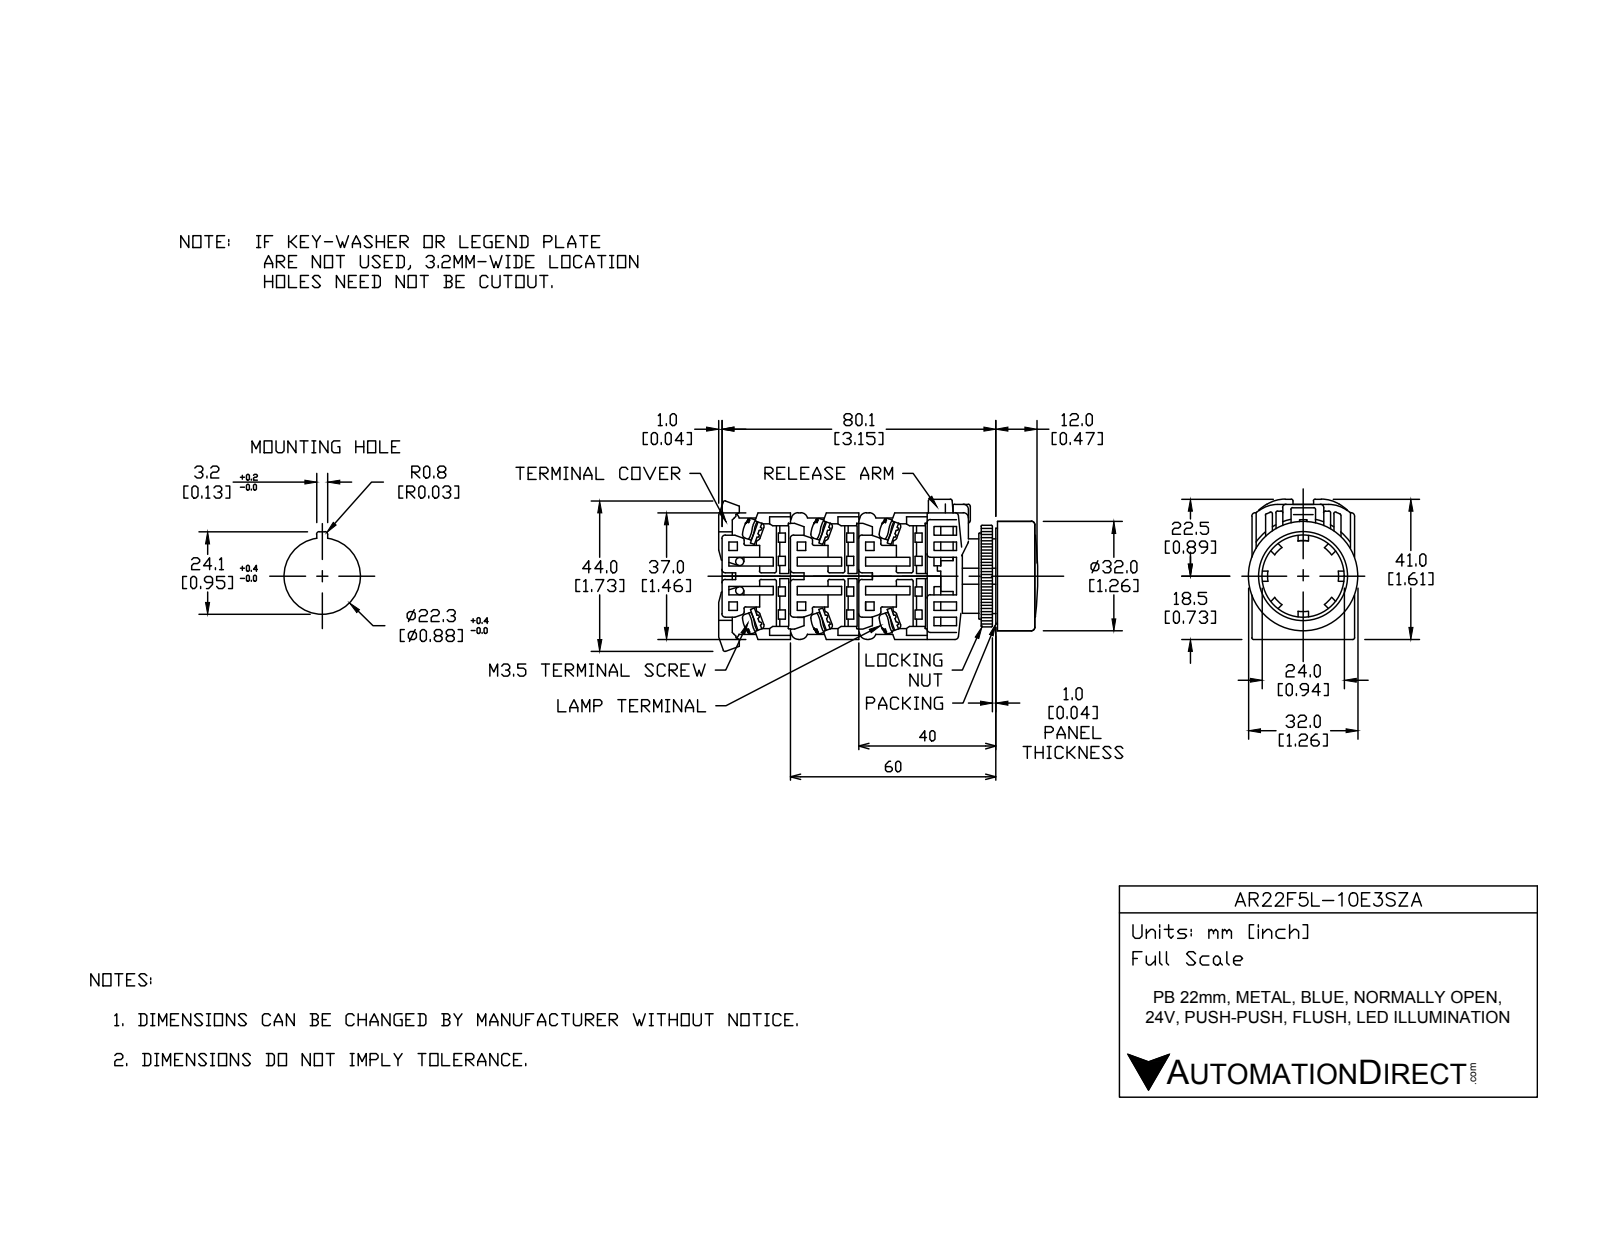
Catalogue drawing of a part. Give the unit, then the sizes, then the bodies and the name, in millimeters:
Units: millimetres
Overall size (bounding box): 52.75 × 43.81 × 32
Round holes (diameter × count): ⌀21.8 ×1, ⌀22 ×1, ⌀25 ×1, ⌀31 ×1
Round bosses / shafts (diameter × count): ⌀5 ×4, ⌀32 ×1, ⌀30.5 ×1, ⌀29.8 ×1, ⌀24 ×1, ⌀23.8 ×1, ⌀21.75 ×1, ⌀17 ×1
Partial cylindrical surfaces — rounded edges, fillets, slot ends (radius × count): R0.5 ×39, R1.75 ×8, R5 ×4, R4 ×2, R16.59 ×1, R17.59 ×1
Main face-to-face distances: 1, 18, 28.5, 48.5, 20, 29, 3, 2, 21, 0.5
Volume: 36 367 mm³ · Surface area: 24 064 mm²
Bodies: 18 solids, 475 faces (329 planar, 111 cylindrical, 35 other)
Part name (STEP PRODUCT): AR22F5L-10E3SZA
STEP written by: SolidWorks 2017 (AUTOMOTIVE_DESIGN)
